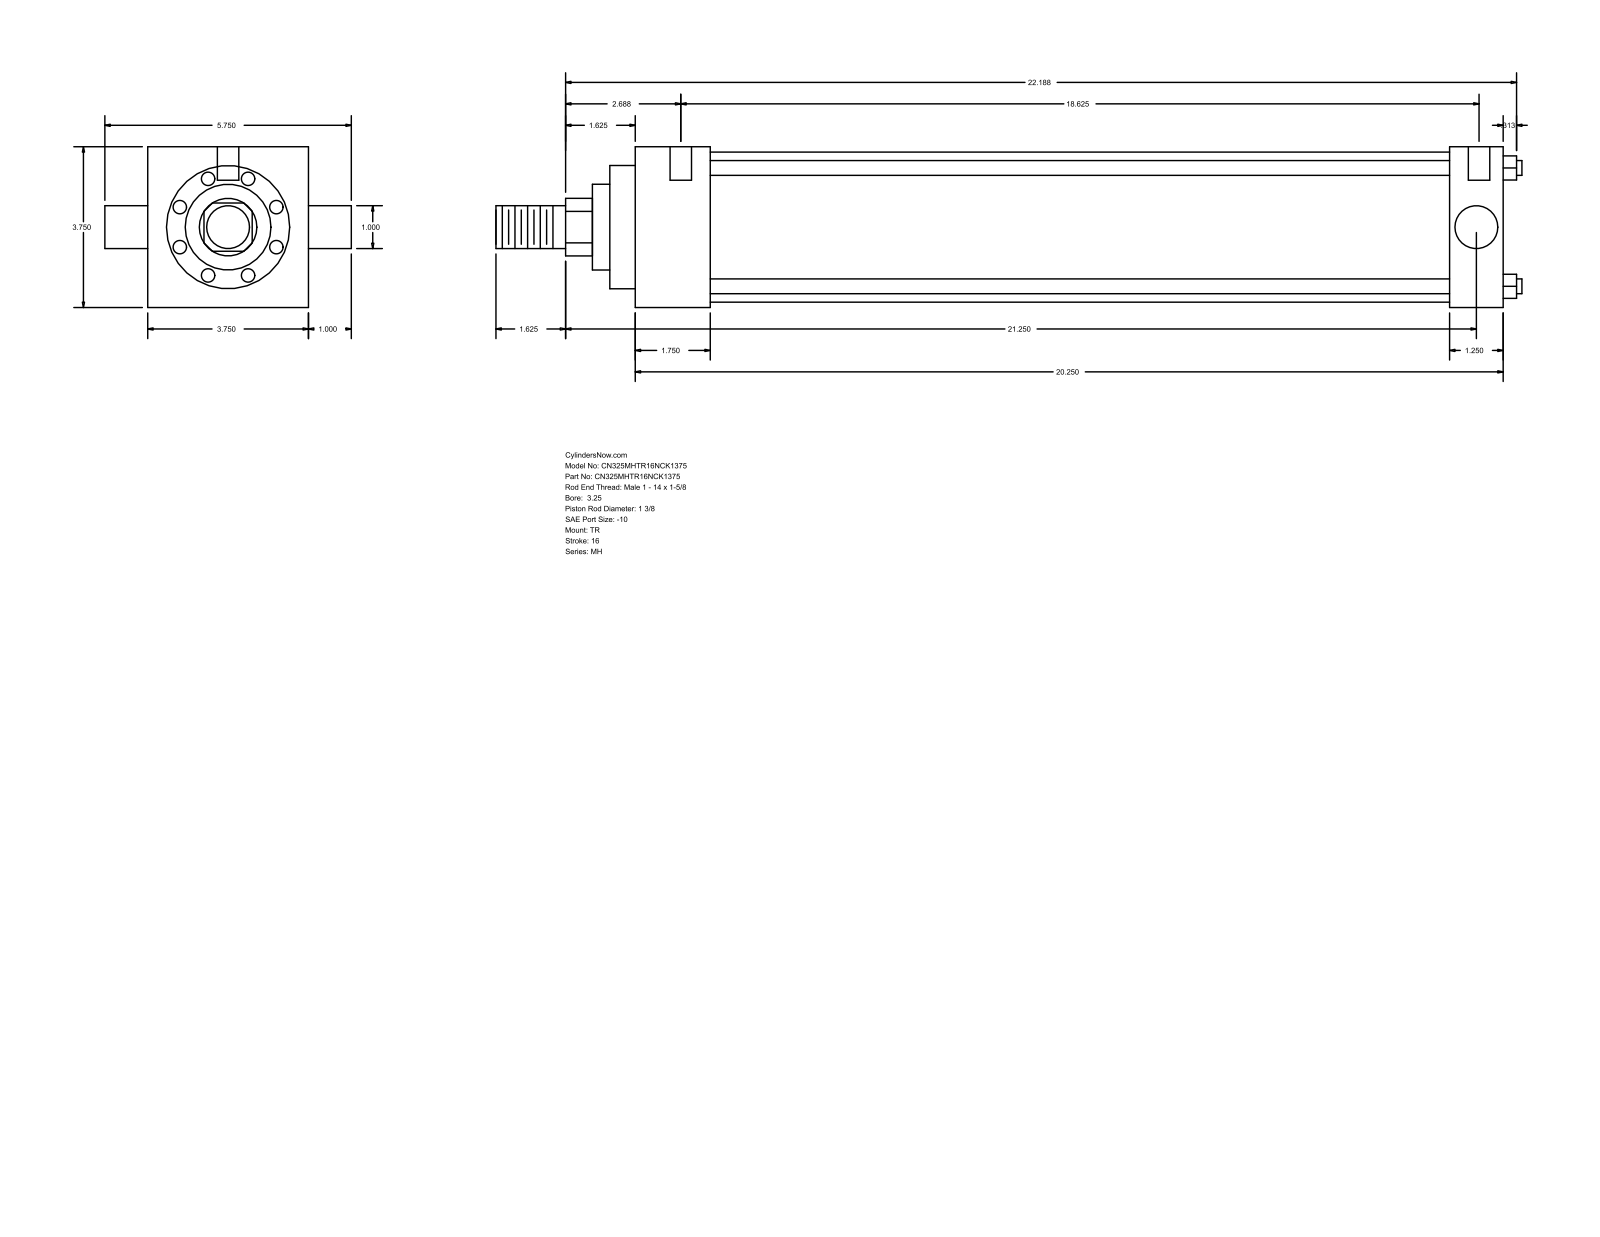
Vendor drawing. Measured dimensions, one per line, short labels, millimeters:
name: MH_TR__0325_1.375
written by: GSSL Pune (CONFIG_CONTROL_DESIGN)
unit: mm
bodies: 0 solids, 86 faces (61 planar, 25 cylindrical, 0 other)
size: 608.01 × 146.05 × 95.25
holes: 3× ⌀5.56, 2× ⌀12.7
bosses: 4× ⌀8.76, 2× ⌀25.4, 1× ⌀88.9, 1× ⌀73.03, 1× ⌀50.8, 1× ⌀34.92
rounds: 1× R17.06
face distances: 95.24, 514.35, 44.45, 482.61, 438.16, 469.9, 31.74, 15.08, 59.53, 497.69
hole spacings: 1.59, 4.76, 473.08, 474.67, 477.84, 479.43
